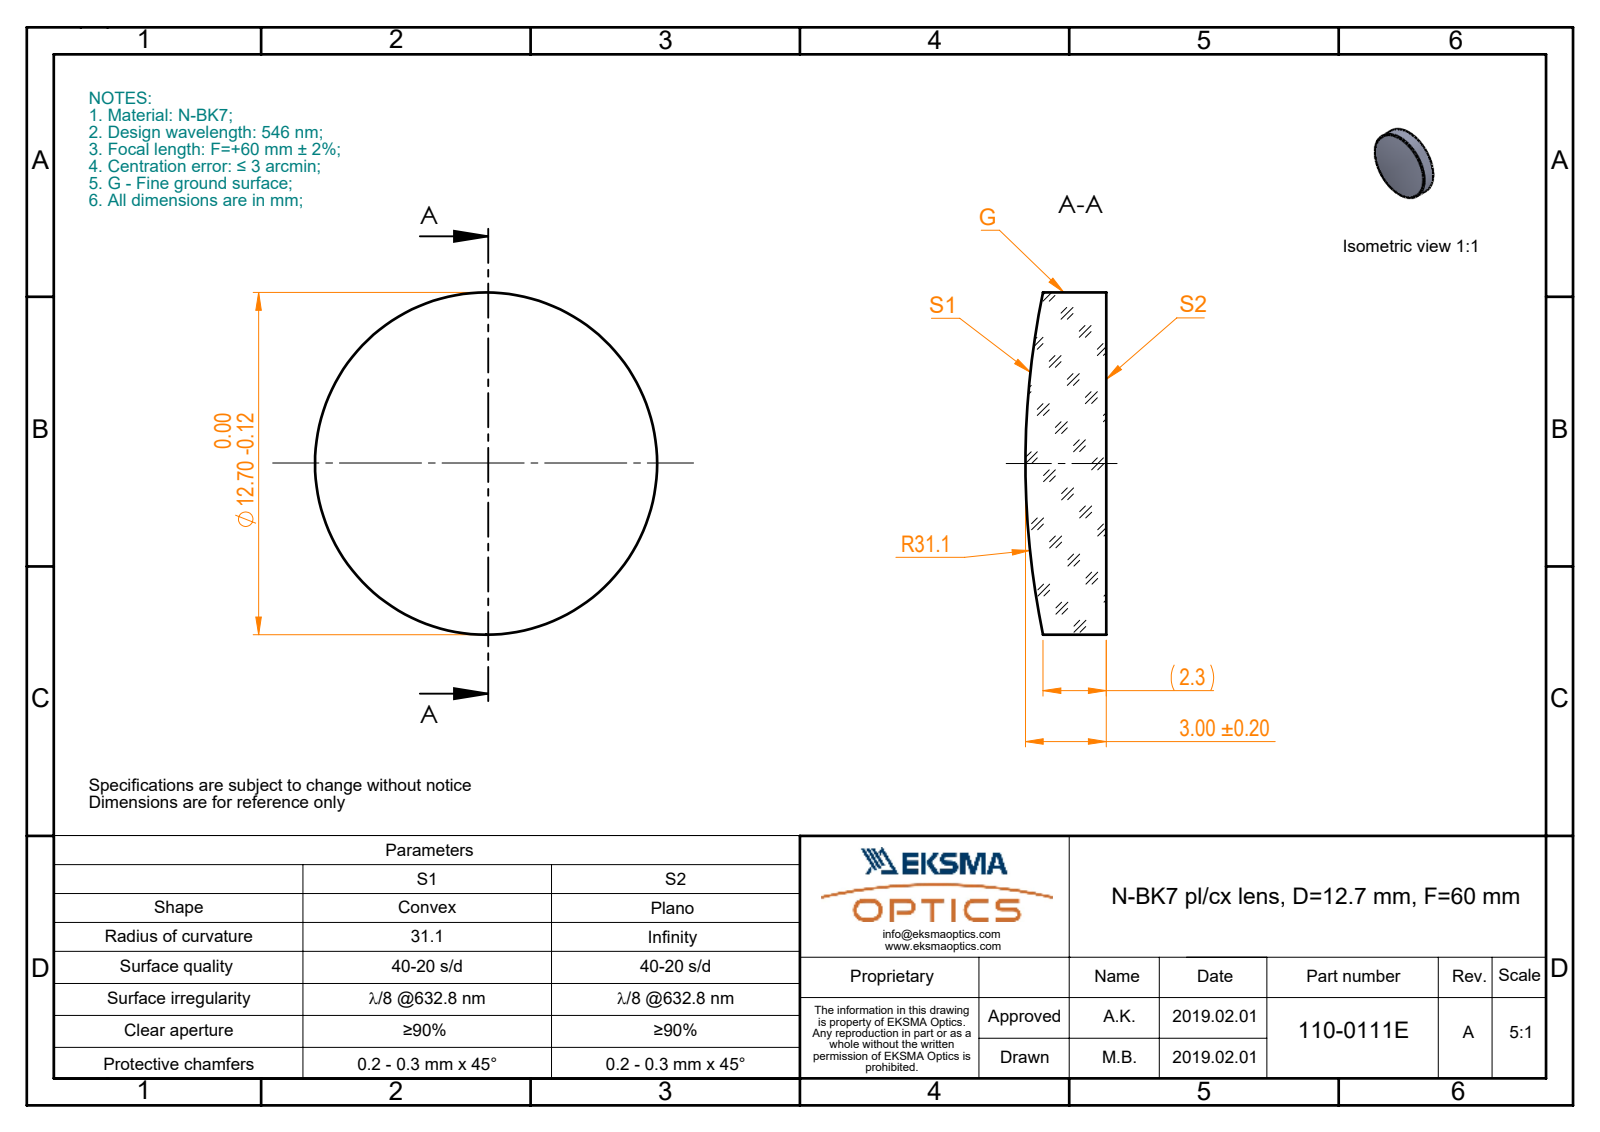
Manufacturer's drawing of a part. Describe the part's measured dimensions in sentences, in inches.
The part is named "110-0111E BK7 pl-cx 12.7 F60". Its 3-D file was written by "SolidWorks 2017 (CONFIG_CONTROL_DESIGN)". It is 1 solid with 5 faces: 1 planar, 2 cylindrical and 2 other. Overall it measures 0.5 by 0.5 by 0.118 inches. Its volume is 0.021 cubic inches and its surface area 0.539 square inches. Round bosses or shafts: 1 of diameter 0.5.
